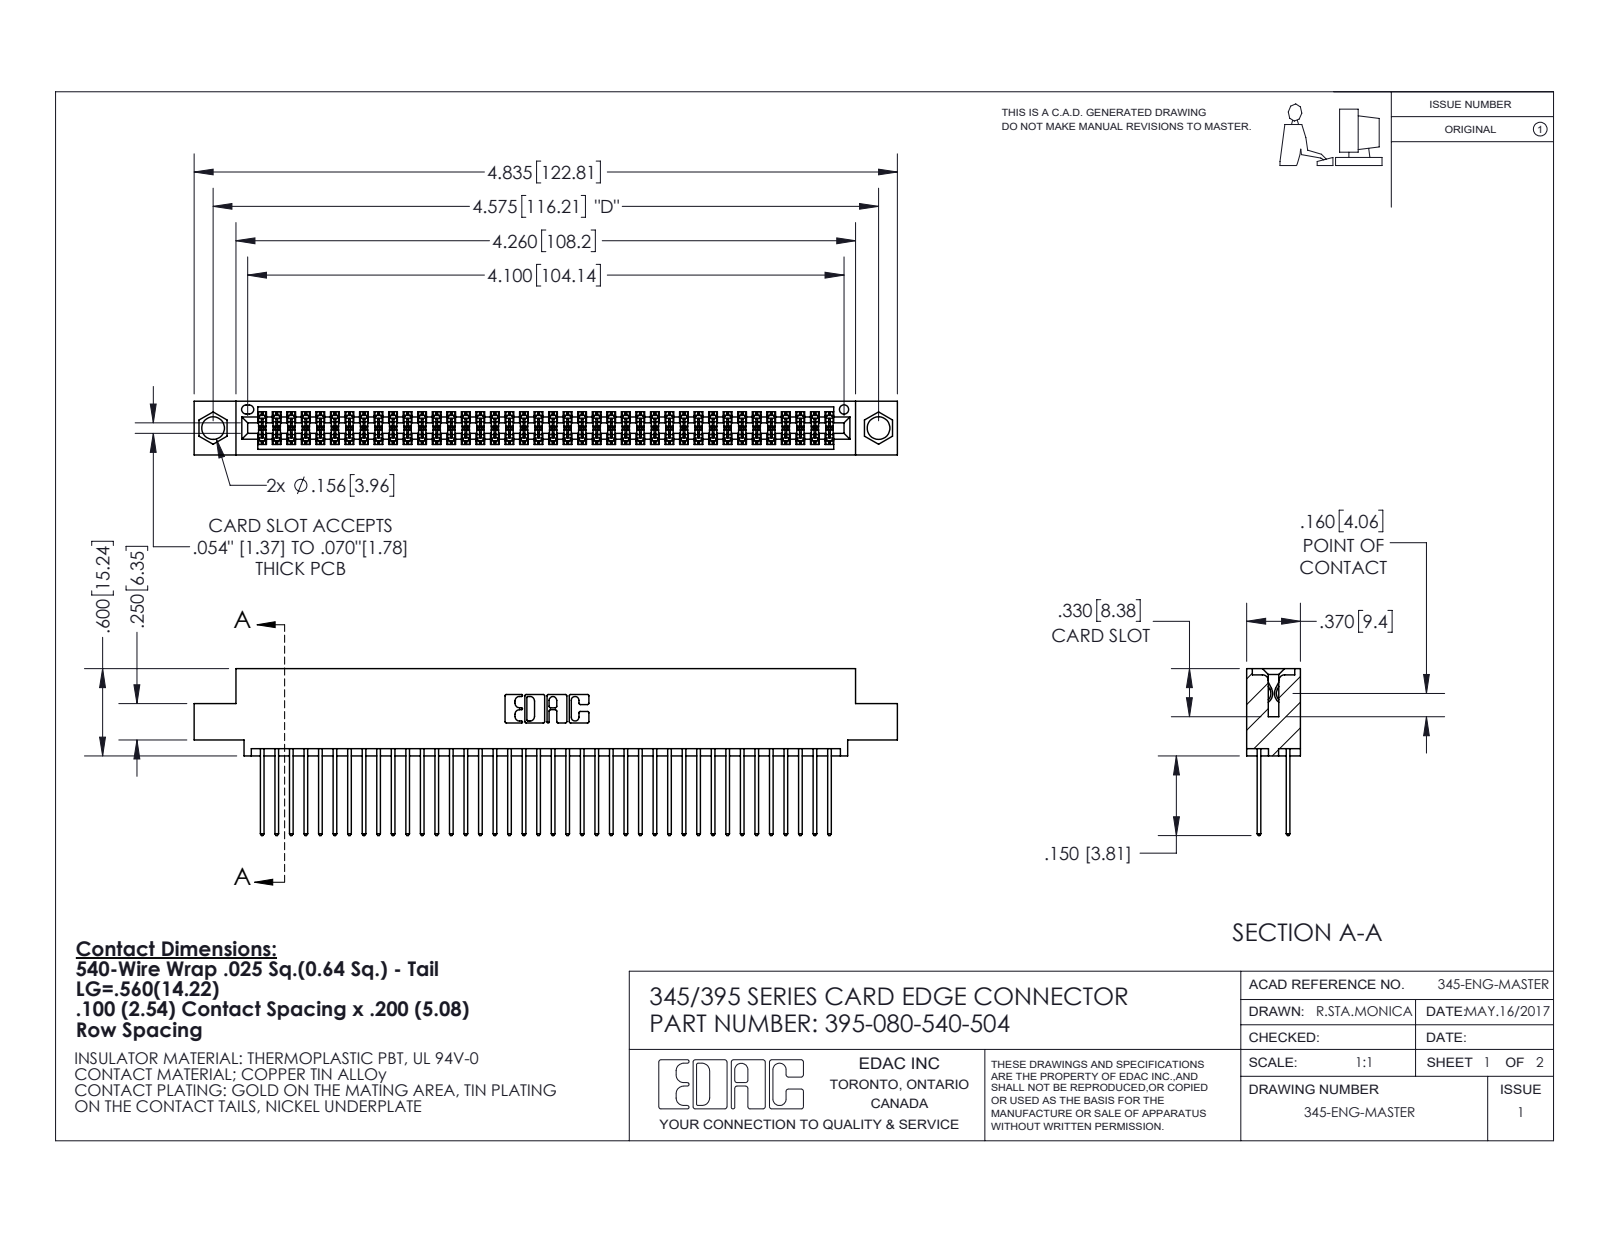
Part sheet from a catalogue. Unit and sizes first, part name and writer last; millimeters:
Units: millimetres
Overall size (bounding box): 122.8 × 29.1 × 9.4
Round holes (diameter × count): ⌀4 ×2, ⌀1.6 ×1
Partial cylindrical surfaces — rounded edges, fillets, slot ends (radius × count): R0.2 ×120, R0.3 ×80, R0.3 ×22, R0.2 ×6, R0.8 ×6, R0.7 ×3, R0.4 ×2, R0.5 ×2
Main face-to-face distances: 7.6, 1.8, 5.1, 2.5, 6.9, 0.6, 9.4, 5.7, 4.4, 3.8
Hole centre spacings: 6.9, 110.2, 116.2
Volume: 12 000 mm³ · Surface area: 19 100 mm²
Bodies: 81 solids, 4144 faces (2738 planar, 1406 cylindrical, 0 other)
Part name (STEP PRODUCT): 345 Part_0.110 Offset - 0.156 Dia-TI; 345-292-001_345-293-140; 395-080-540-504
STEP written by: SolidWorks 2020 (CONFIG_CONTROL_DESIGN)
